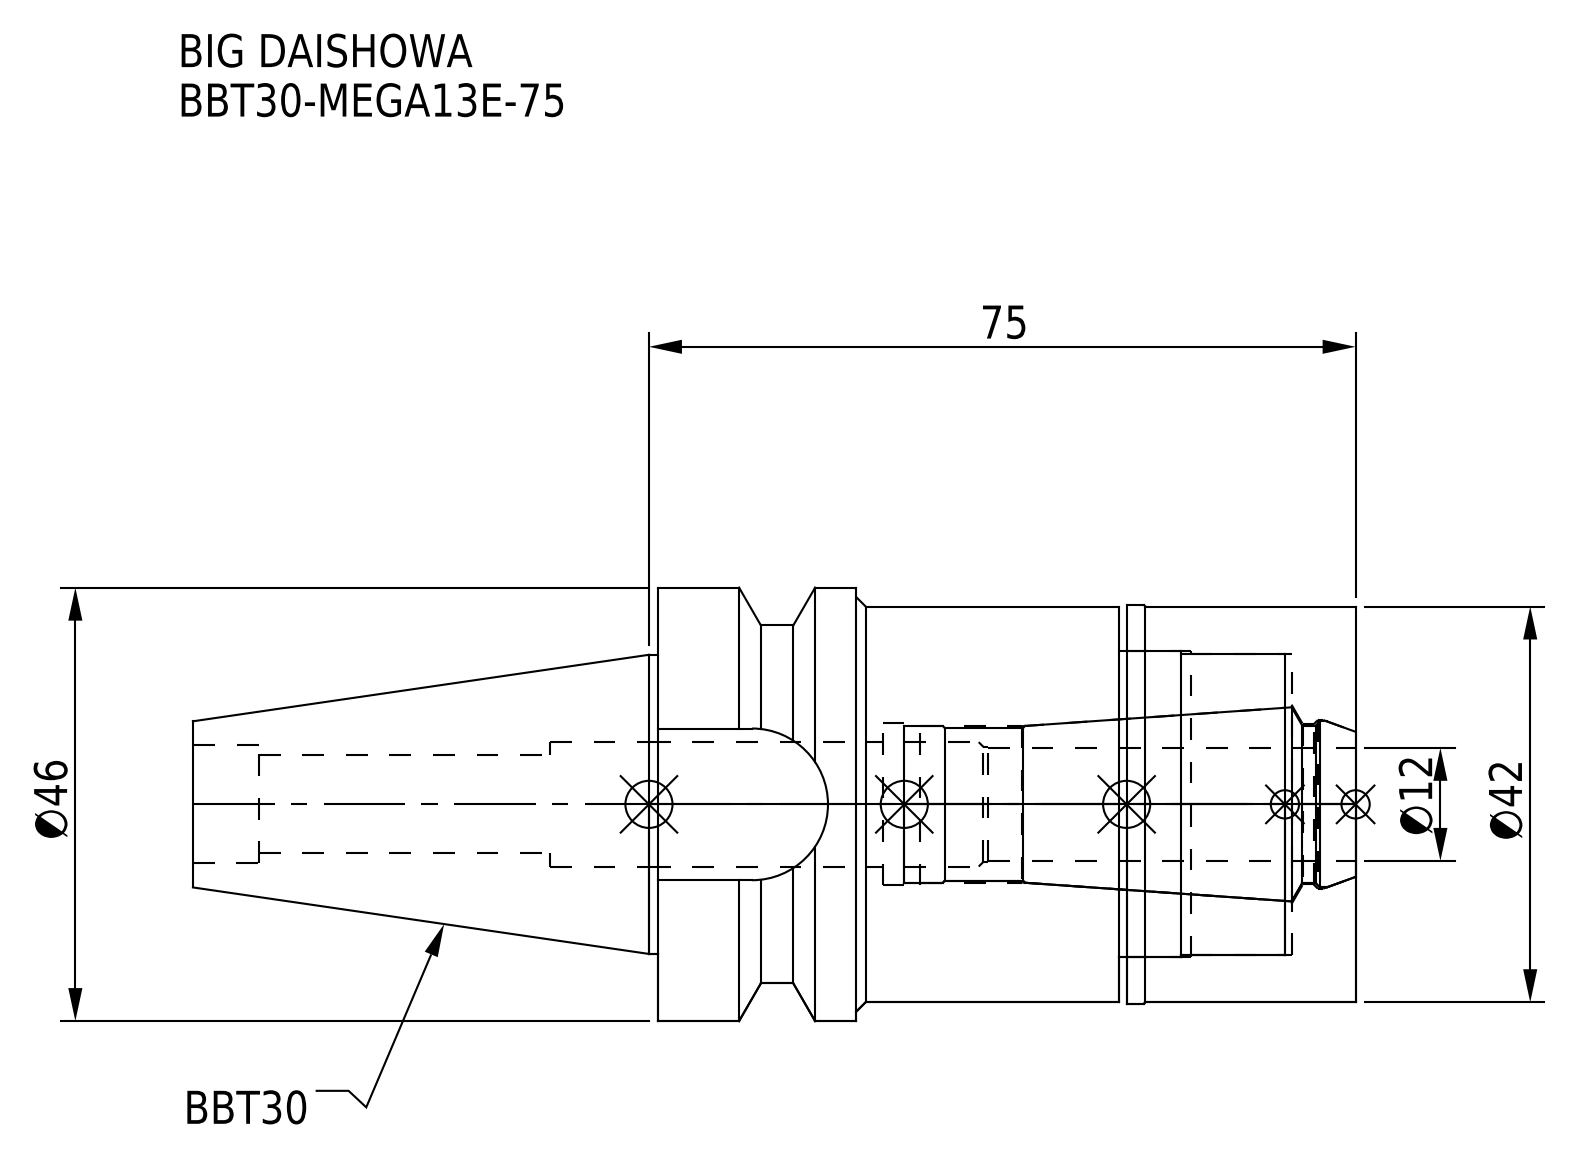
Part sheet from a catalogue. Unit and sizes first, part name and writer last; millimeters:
Units: millimetres
Overall size (bounding box): 123.4 × 46 × 46
Round holes (diameter × count): ⌀10.4 ×1, ⌀12.5 ×1, ⌀13.3 ×1, ⌀16.6 ×1, ⌀17 ×1, ⌀17.2 ×1, ⌀17.9 ×1, ⌀32 ×1, ⌀32.5 ×1
Round bosses / shafts (diameter × count): ⌀46 ×1, ⌀42.3 ×1, ⌀42 ×1, ⌀31.75 ×1
Partial cylindrical surfaces — rounded edges, fillets, slot ends (radius × count): R8.05 ×1, R19 ×1
Main face-to-face distances: 74, 25.1, 24.3, 49.7, 0.8, 48.9, 6.8, 17.5, 7.5, 16.8
Volume: 105 504 mm³ · Surface area: 28 234 mm²
Bodies: 2 solids, 78 faces (20 planar, 40 cylindrical, 18 other)
Part name (STEP PRODUCT): BBT30-MEGA13E-75; BBT30-MEGA13E-75_1.stp; BBT30ME13075-120_ASM.stp; BBT30-MEGA13E-75-120-FreeParts (+3 more)
STEP written by: SolidWorks 2019 (CONFIG_CONTROL_DESIGN)
